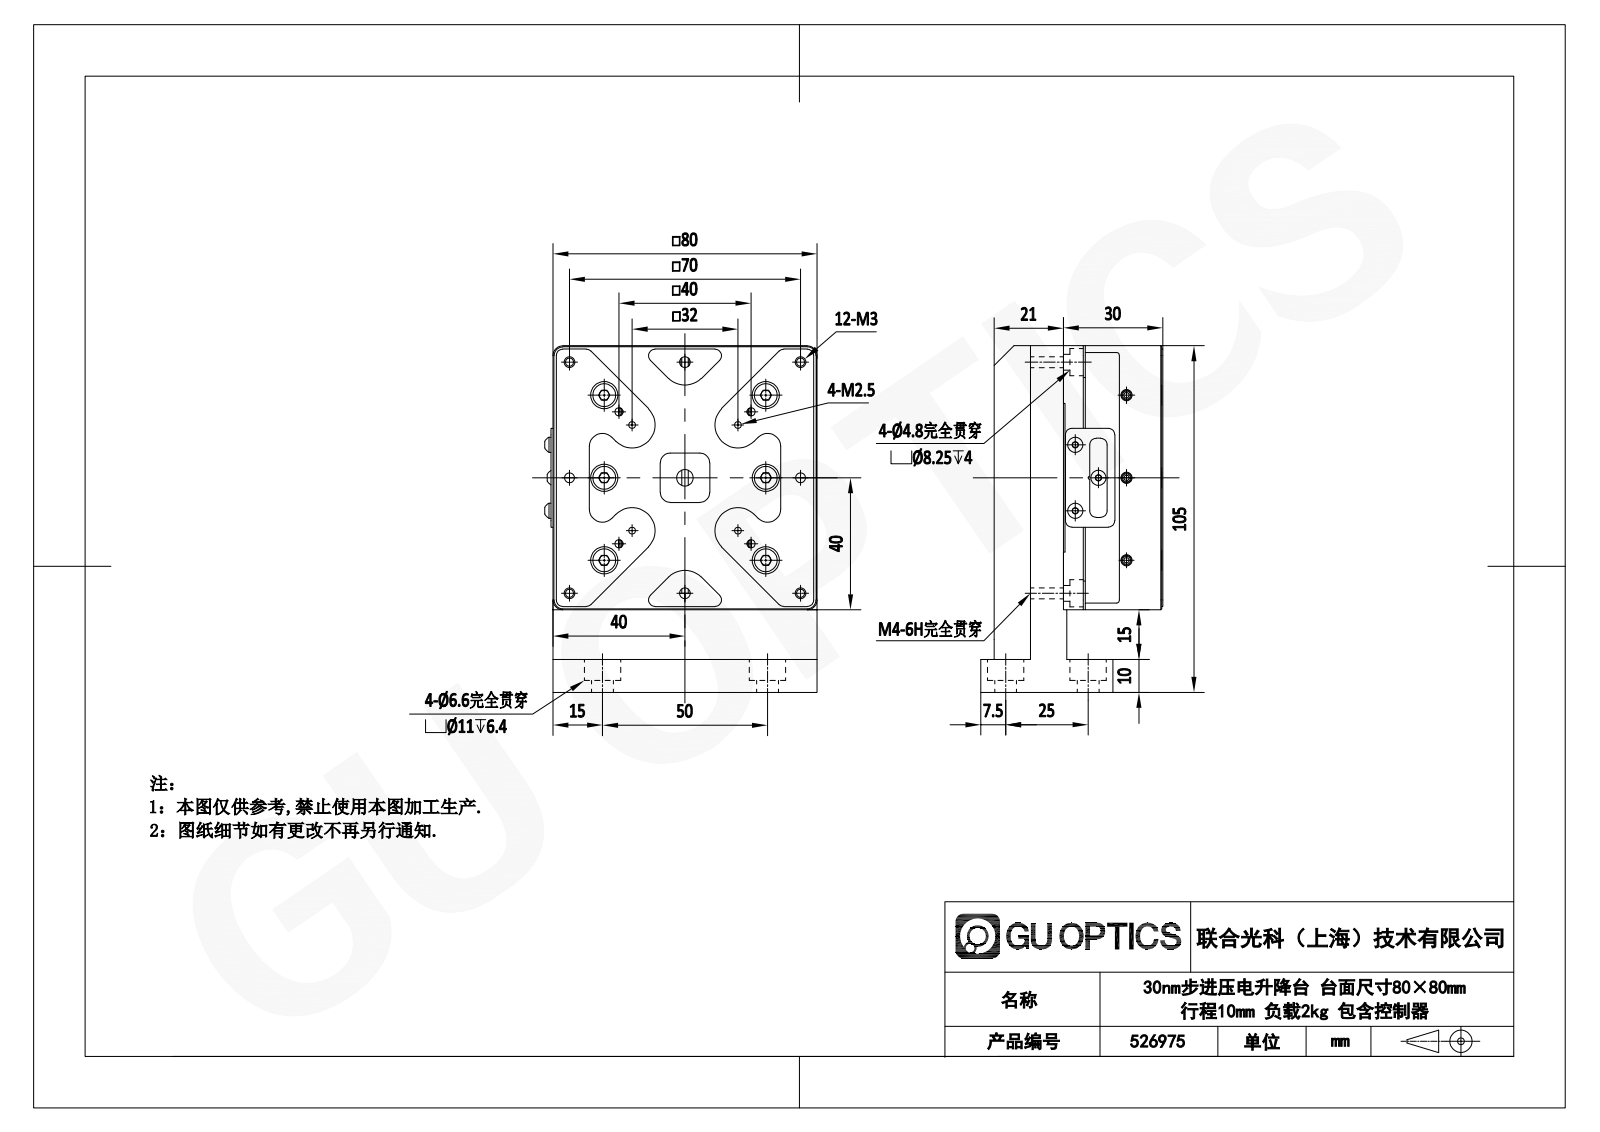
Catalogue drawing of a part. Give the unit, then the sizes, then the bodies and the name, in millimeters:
Units: millimetres
Overall size (bounding box): 105 × 82.5 × 55.11
Round holes (diameter × count): ⌀3.3 ×18, ⌀2.5 ×17, ⌀6 ×12, ⌀8.25 ×10, ⌀2.05 ×7, ⌀4.5 ×6, ⌀2.9 ×5, ⌀5.2 ×5, ⌀3 ×4, ⌀4.8 ×4, ⌀6.6 ×4, ⌀11 ×4
Round bosses / shafts (diameter × count): ⌀3 ×25, ⌀2.5 ×8, ⌀7 ×6, ⌀4 ×6, ⌀4.7 ×5, ⌀4.6 ×3, ⌀5.5 ×2
Partial cylindrical surfaces — rounded edges, fillets, slot ends (radius × count): R2.5 ×34, R2 ×33, R3 ×16, R4 ×8, R0.8 ×6, R1 ×6, R1.5 ×6, R7 ×6
Main face-to-face distances: 15, 10, 0.5, 25, 15.11, 80, 11, 11.8, 8.61, 0.6
Hole centre spacings: 25, 35, 24.84, 27.31, 36.22, 41.08, 45.49, 49.5
Volume: 312 130 mm³ · Surface area: 102 727 mm²
Bodies: 35 solids, 1750 faces (872 planar, 481 cylindrical, 397 other)
Part name (STEP PRODUCT): 526961
STEP written by: SolidWorks 2020 (CONFIG_CONTROL_DESIGN)
